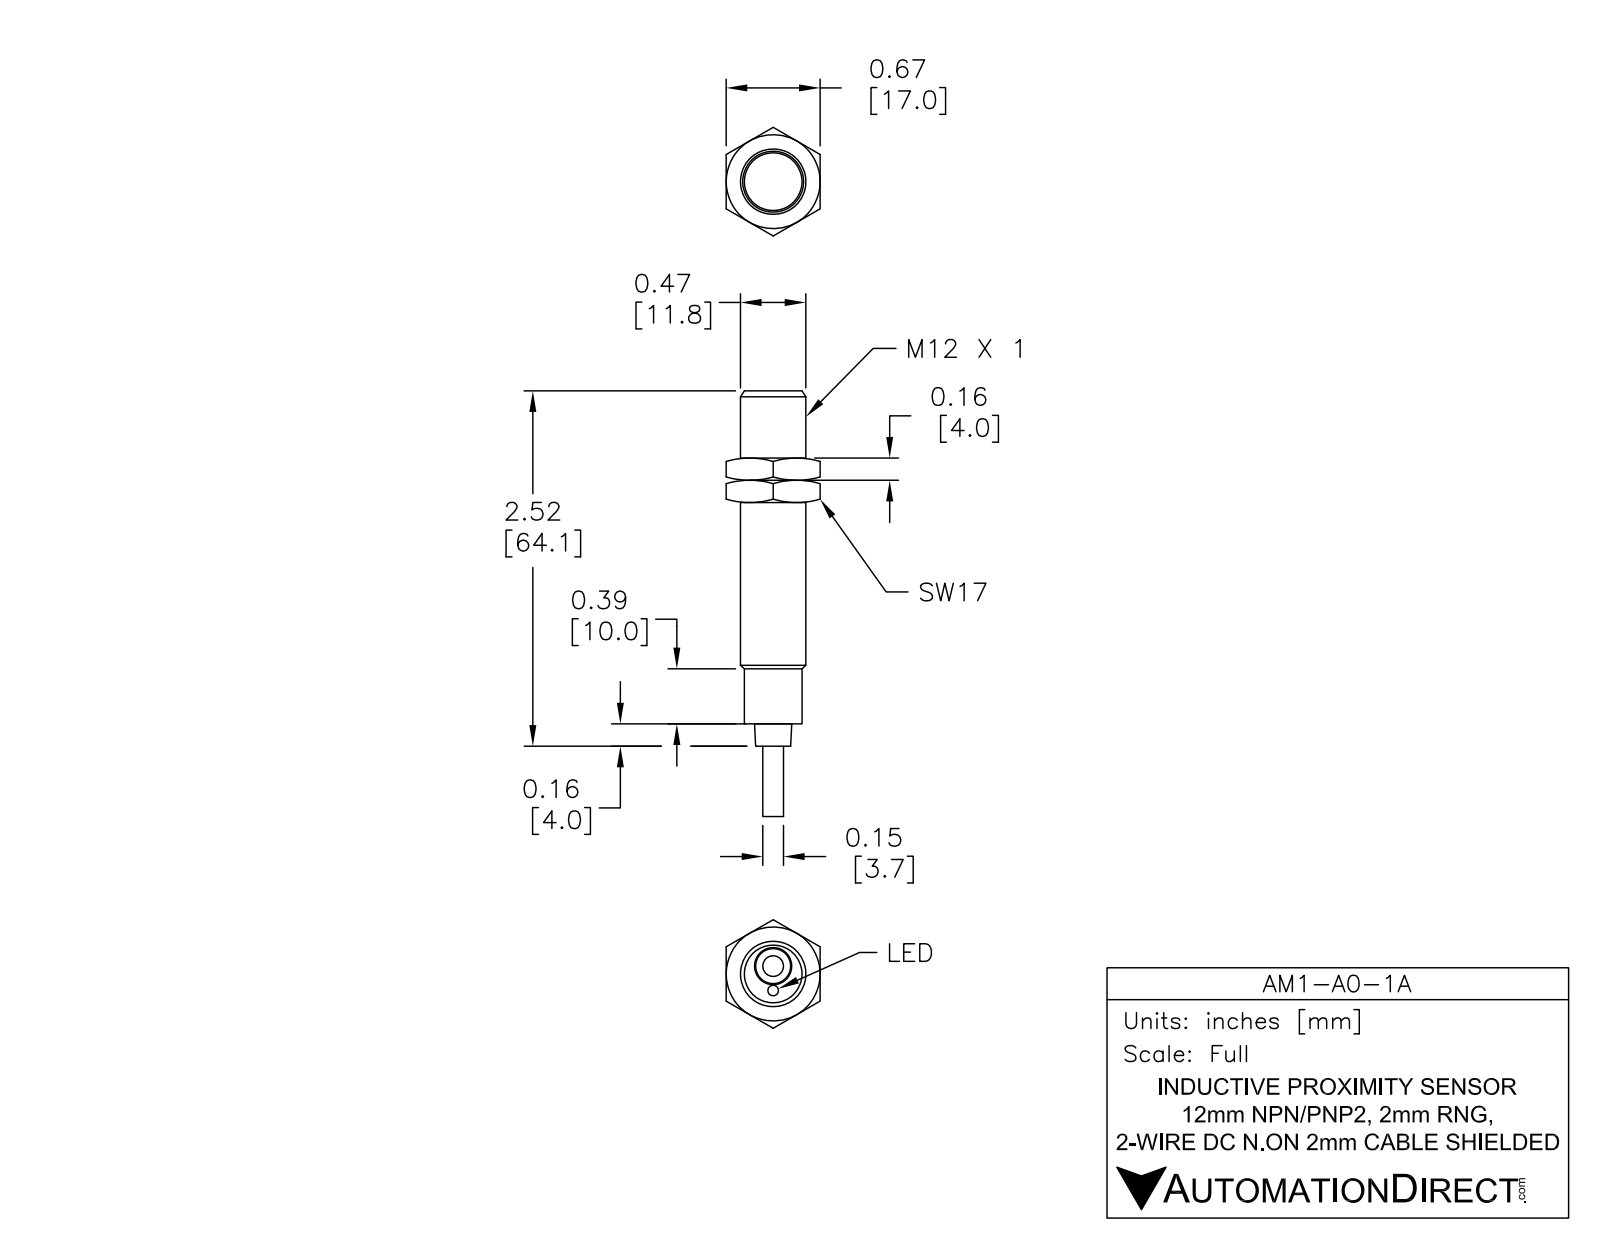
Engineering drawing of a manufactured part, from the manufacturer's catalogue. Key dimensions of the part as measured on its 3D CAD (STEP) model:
Part name (STEP PRODUCT): AM1-A0-1A
STEP written by: SolidWorks 2017 (AUTOMOTIVE_DESIGN)
Units: inches
Bodies: 4 solids, 46 faces (21 planar, 13 cylindrical, 12 other)
Overall size (bounding box): 4.039 × 0.472 × 0.472
Volume: 0.428 in³ · Surface area: 5.143 in²
Round holes (diameter × count): ⌀0.15 ×1
Round bosses / shafts (diameter × count): ⌀0.472 ×1, ⌀0.413 ×1, ⌀0.148 ×1
Partial cylindrical surfaces — rounded edges, fillets, slot ends (radius × count): R0.047 ×2, R0.203 ×1
Main face-to-face distances: 1.949, 0.02, 1.969, 2.354, 2.335, 0.386, 2.465, 2.445, 0.496, 0.11
